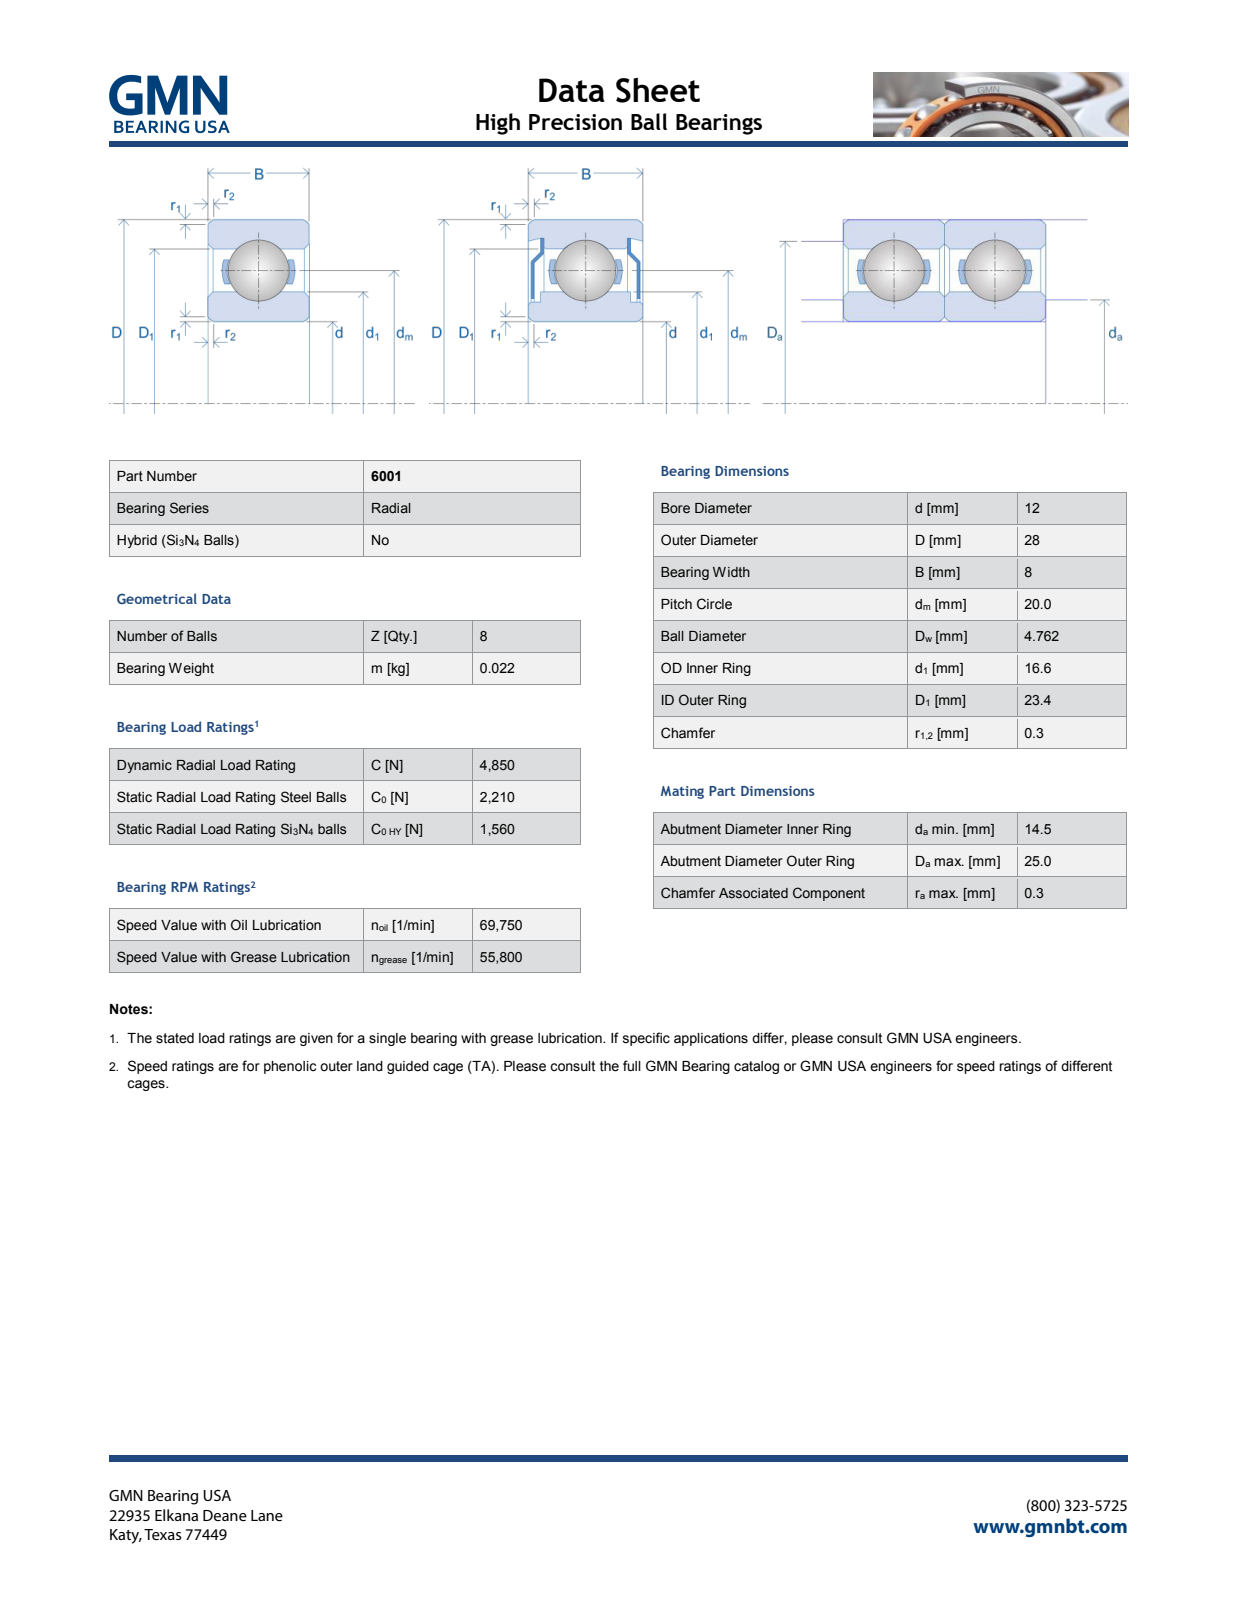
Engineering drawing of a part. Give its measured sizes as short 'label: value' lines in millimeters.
name: 6001_PRT
written by: PRO/ENGINEER BY PARAMETRIC TECHNOLOGY CORPORATION, 2013150 (AUTOMOTIVE_DESIGN)
unit: mm
bodies: 11 solids, 510 faces (442 planar, 32 cylindrical, 36 other)
size: 28 × 28 × 8.01
volume: 3 098 mm³; area: 4 243 mm²
holes: 4× ⌀4.96, 1× ⌀12, 1× ⌀19.6, 1× ⌀23.4
bosses: 1× ⌀28, 1× ⌀22.6, 1× ⌀16.65
face distances: 8, 7.9, 7.8, 7.91, 8.01, 1.3, 1.14, 0.97, 0.92, 1.13
